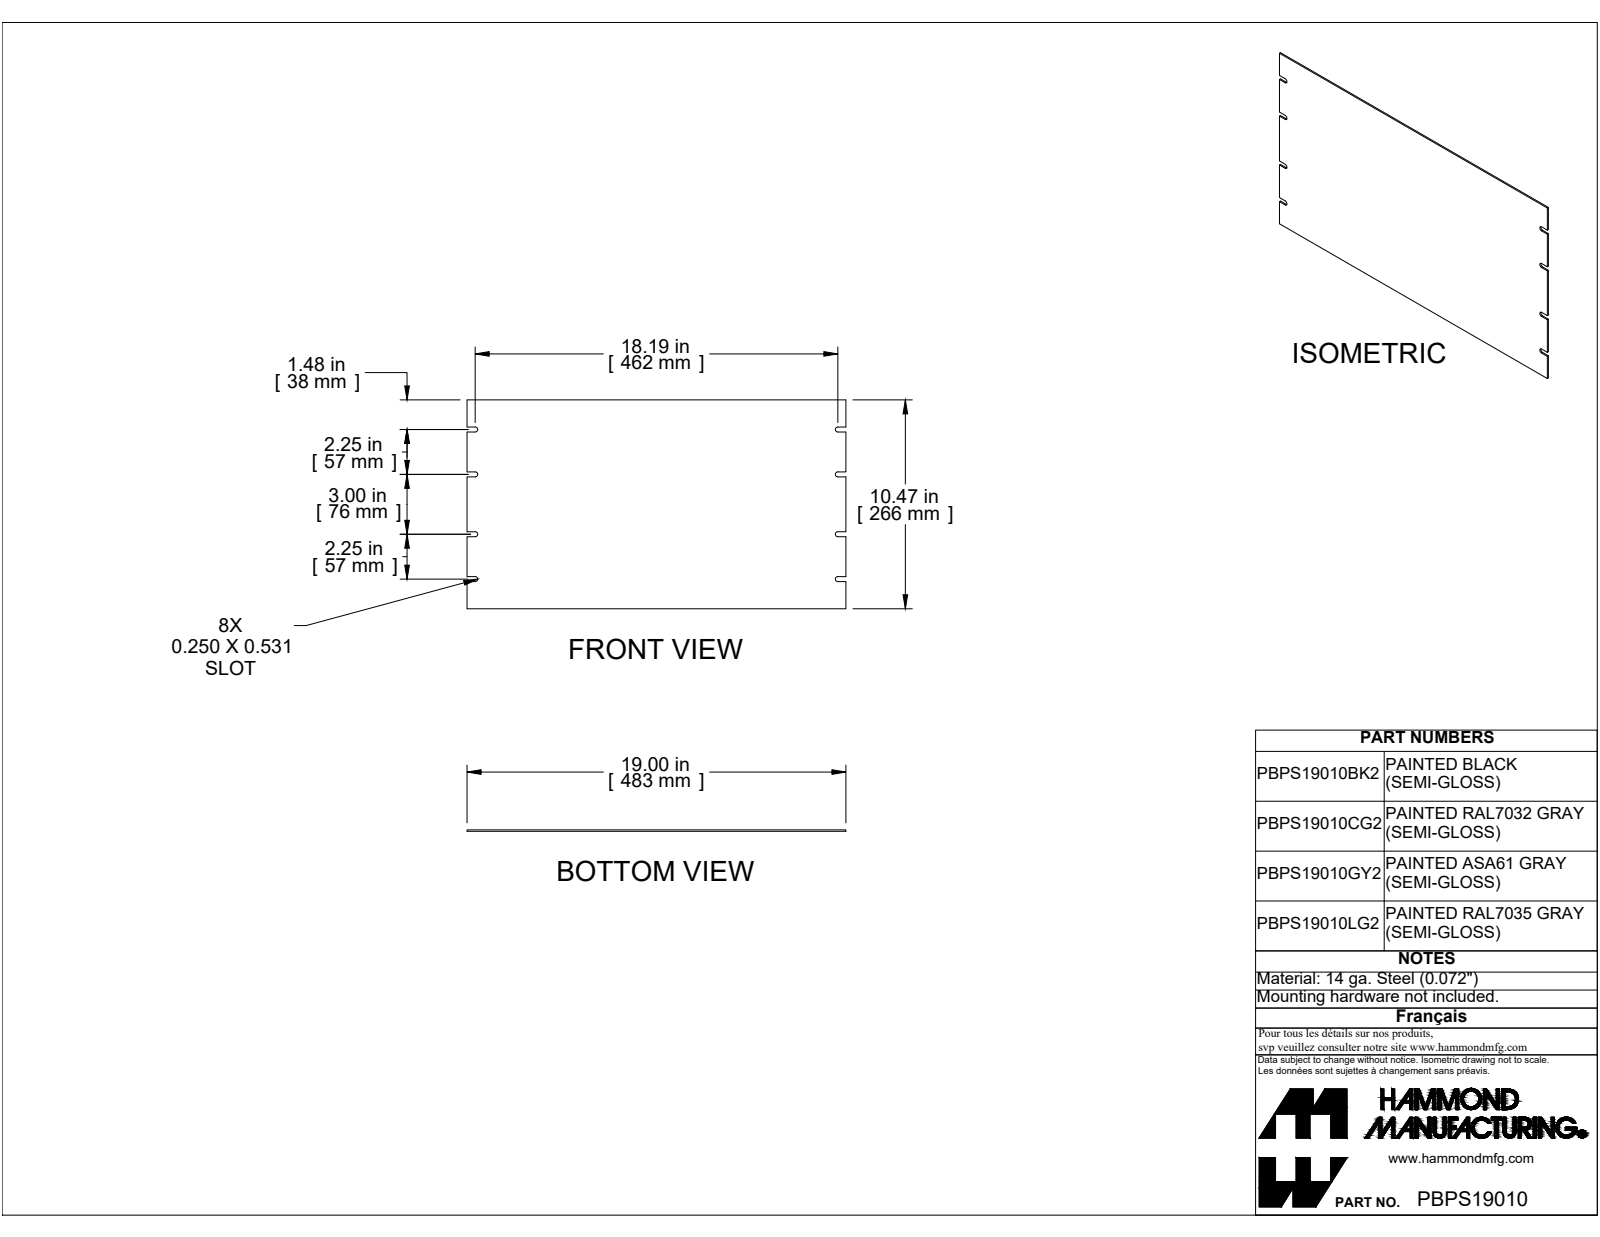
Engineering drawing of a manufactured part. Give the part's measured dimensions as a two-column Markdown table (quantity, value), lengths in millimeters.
| quantity | value |
| --- | --- |
| part name | PBPS19010GY2 |
| STEP written by | SolidWorks 2019 (CONFIG_CONTROL_DESIGN) |
| units | millimeters |
| bodies | 1 solid, 38 faces (30 planar, 8 cylindrical, 0 other) |
| overall size | 482.6 × 265.9 × 1.8 |
| volume | 233 500 mm³ |
| surface area | 258 500 mm² |
| partial cylindrical surfaces (radius × count) | 3.2 × 8 |
| main face-to-face distances | 1.8, 265.9, 482.6, 57.2, 133.4, 6.4, 98, 167.9, 6.4, 57.2 |
